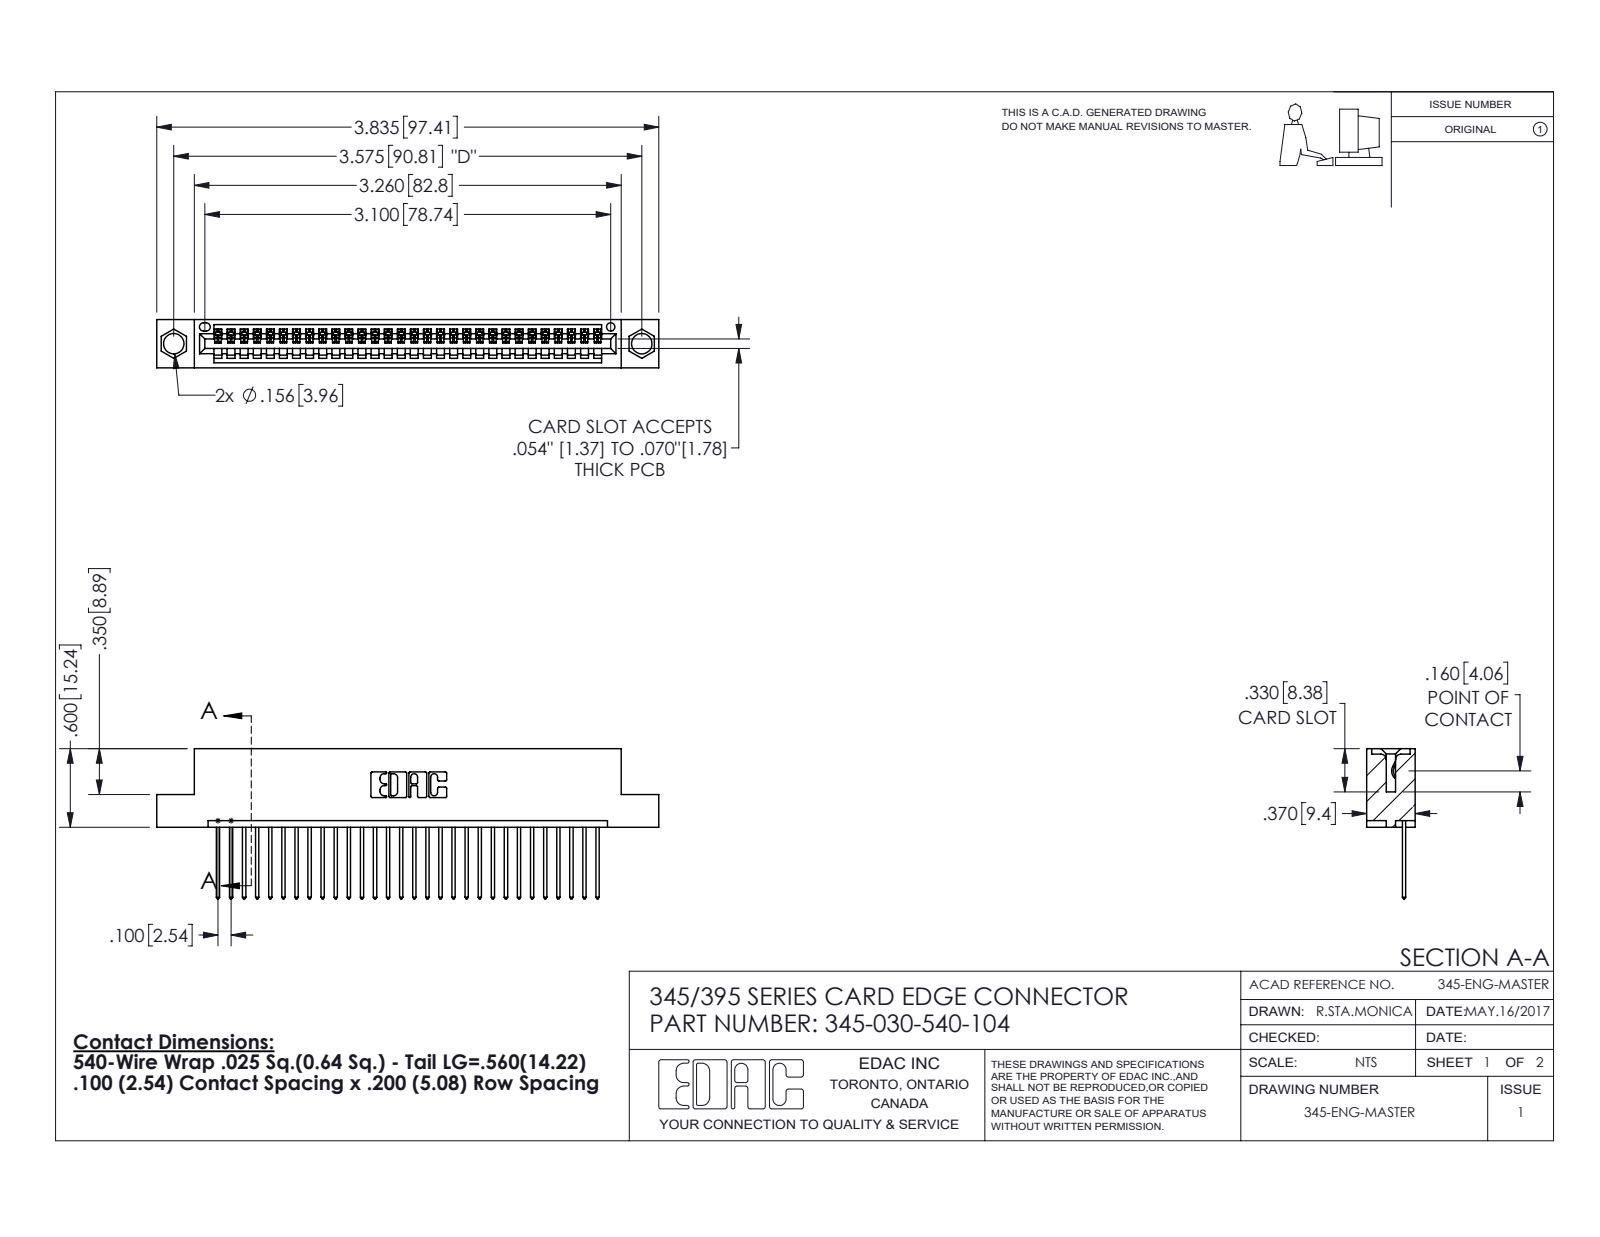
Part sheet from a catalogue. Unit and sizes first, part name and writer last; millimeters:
Units: millimetres
Overall size (bounding box): 97.4 × 29.1 × 9.4
Round holes (diameter × count): ⌀4 ×2, ⌀1.6 ×1
Partial cylindrical surfaces — rounded edges, fillets, slot ends (radius × count): R0.2 ×60, R0.3 ×60, R0.3 ×22, R0.2 ×6, R0.8 ×6, R0.7 ×3, R0.8 ×2, R1 ×2
Main face-to-face distances: 7.6, 1.8, 5.1, 9.4, 2.5, 6.9, 0.6, 5.7, 3.8, 1.8
Hole centre spacings: 6.9, 84.8, 90.8
Volume: 9 110 mm³ · Surface area: 12 040 mm²
Bodies: 31 solids, 1866 faces (1280 planar, 586 cylindrical, 0 other)
Part name (STEP PRODUCT): 345-030-540-104; 345 Part_Flush Mounting Lugs - 0.156 Dia-TH; 345-292-001_345-293-140
STEP written by: SolidWorks 2016 (CONFIG_CONTROL_DESIGN)
